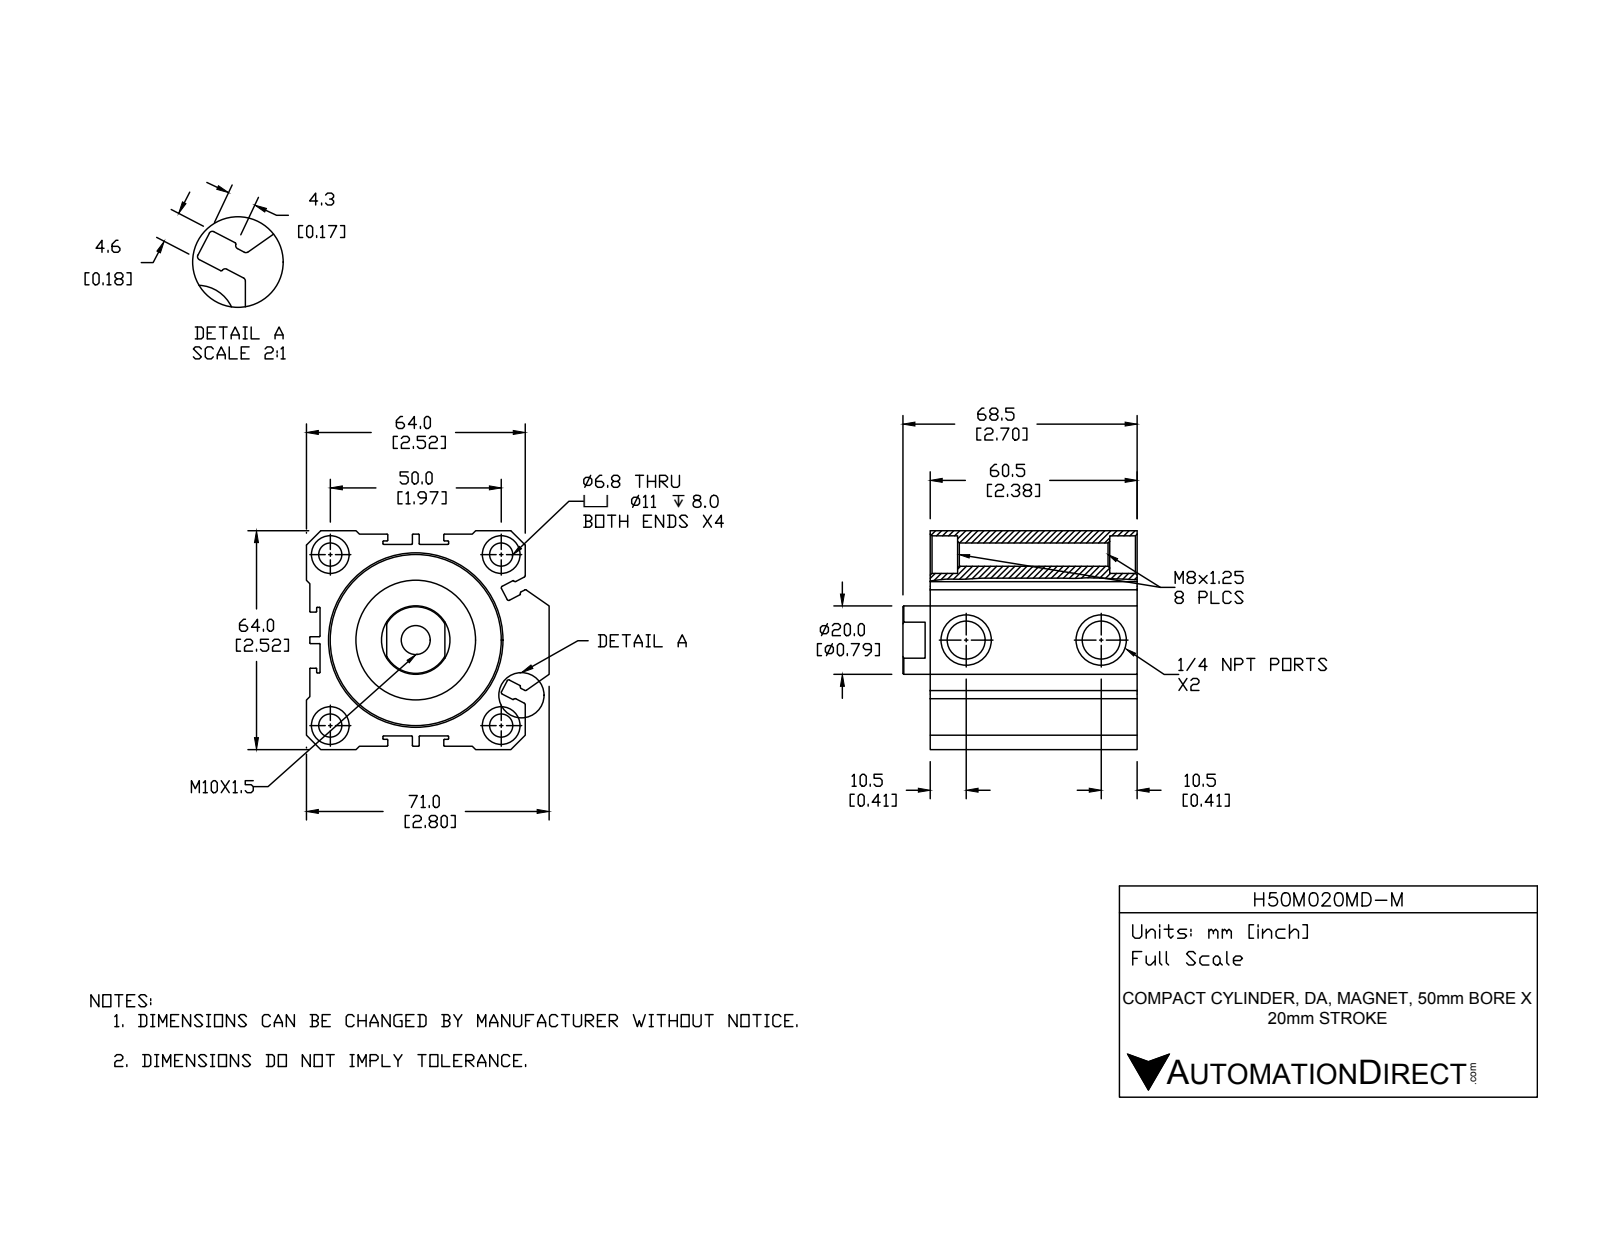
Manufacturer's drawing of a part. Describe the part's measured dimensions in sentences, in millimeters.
The part is named "H50M020MD-M; H50M020MD-M-BODY; H50M020MD-M-PISTON". Its 3-D file was written by "SolidWorks 2015 (CONFIG_CONTROL_DESIGN)". It is 2 solids with 255 faces: 99 planar, 103 cylindrical and 53 other. Overall it measures 71 by 68.5 by 64 millimeters. Its volume is 179 164 cubic millimeters and its surface area 56 853 square millimeters. Round holes: 4 of diameter 6.8, 4 of diameter 11, 2 of diameter 11.13, 1 of diameter 8.5, 1 of diameter 20, 1 of diameter 36, 1 of diameter 50. Round bosses or shafts: 1 of diameter 35, 1 of diameter 31. Partial cylindrical surfaces (rounded edges, fillets, slot ends): 40 of radius 0.2, 12 of radius 0.5. The main face-to-face distances are 4, 60, 1, 3, 63, 30, 7, 64, 2, 1.5. The hole center spacings are 35.36, 50, 70.71, 39.5.
